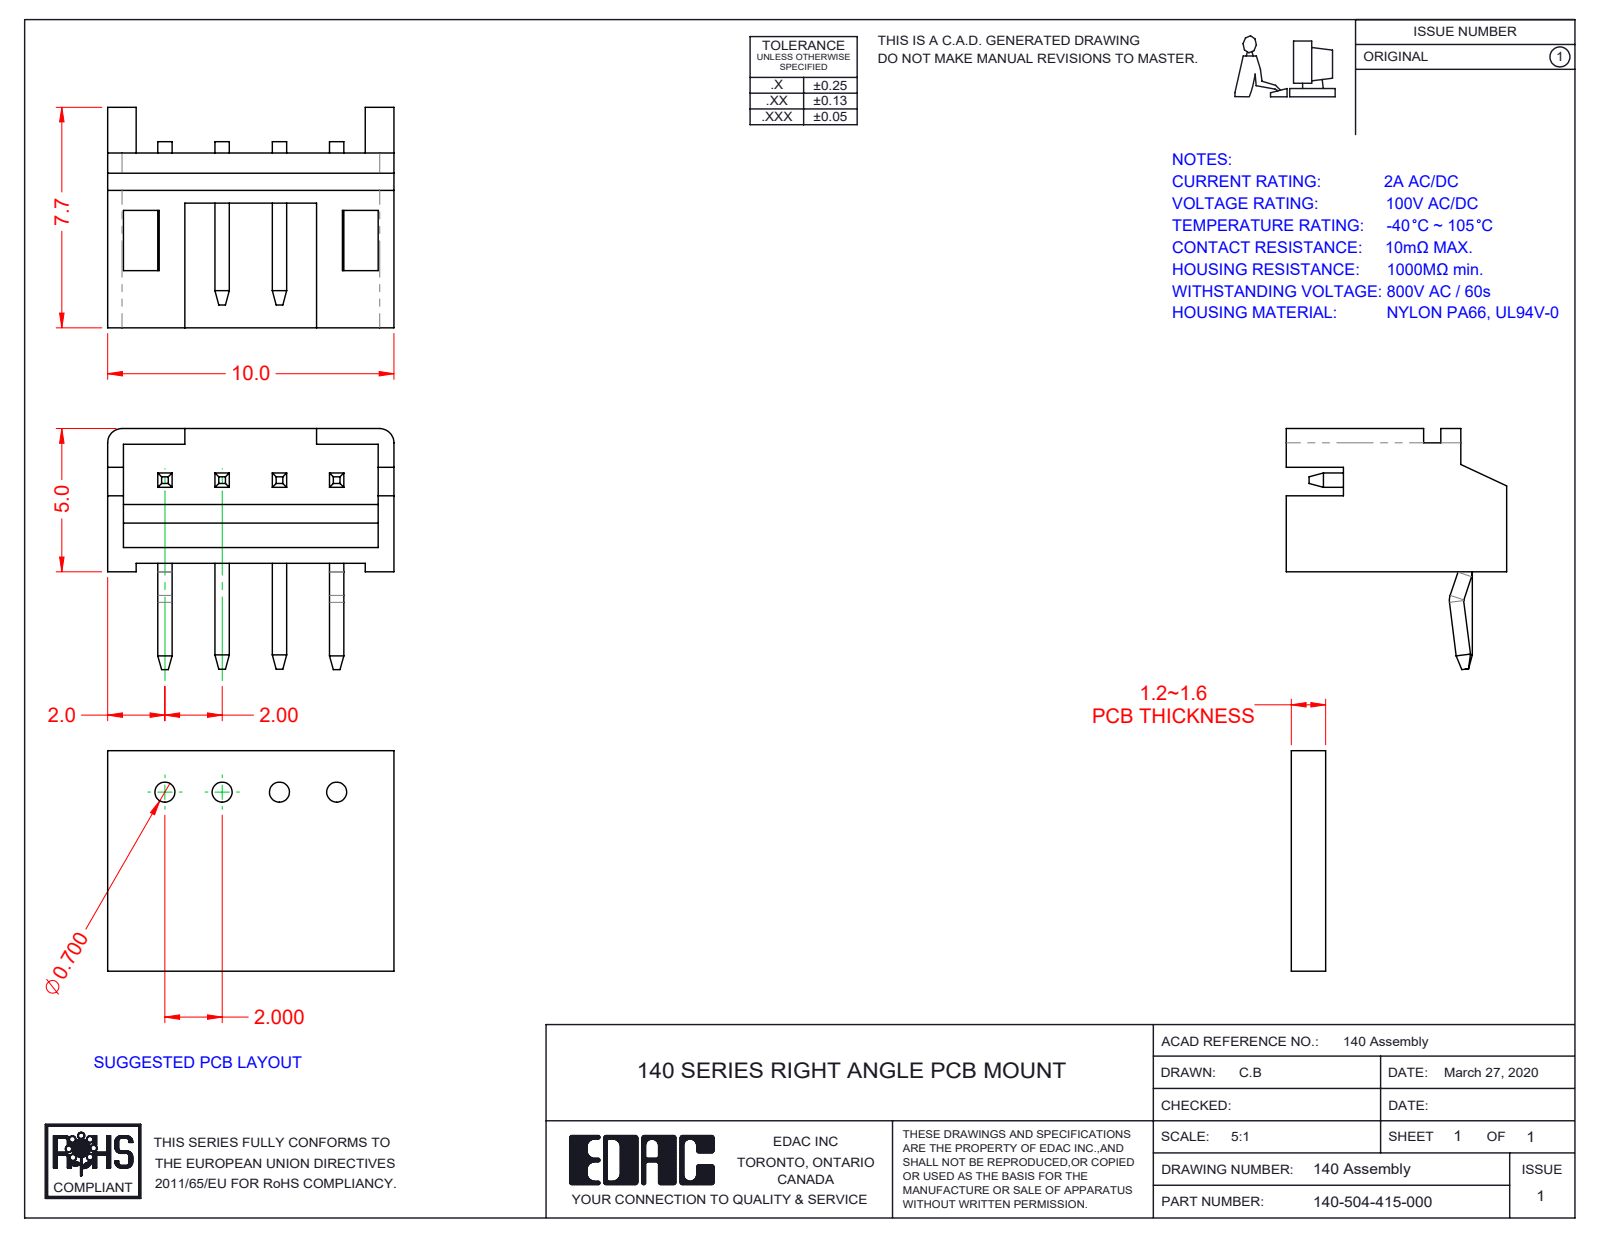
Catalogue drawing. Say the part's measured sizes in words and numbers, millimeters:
The part is named "RA Contact_Str; RA Contact_Kink; RA Housing_504; 140-504-415-000". Its 3-D file was written by "SolidWorks 2016 (CONFIG_CONTROL_DESIGN)". It is 5 solids with 199 faces: 179 planar, 20 cylindrical and 0 other. Overall it measures 10 by 8.41 by 7.7 millimeters. Its volume is 139 cubic millimeters and its surface area 504 square millimeters. Partial cylindrical surfaces (rounded edges, fillets, slot ends): 2 of radius 0.5, 2 of radius 0.55, 1 of radius 0.15, 1 of radius 0.65. The main face-to-face distances are 0.55, 1.5, 0.5, 2, 1, 4.15, 0.45, 1.75, 9.45, 10.
